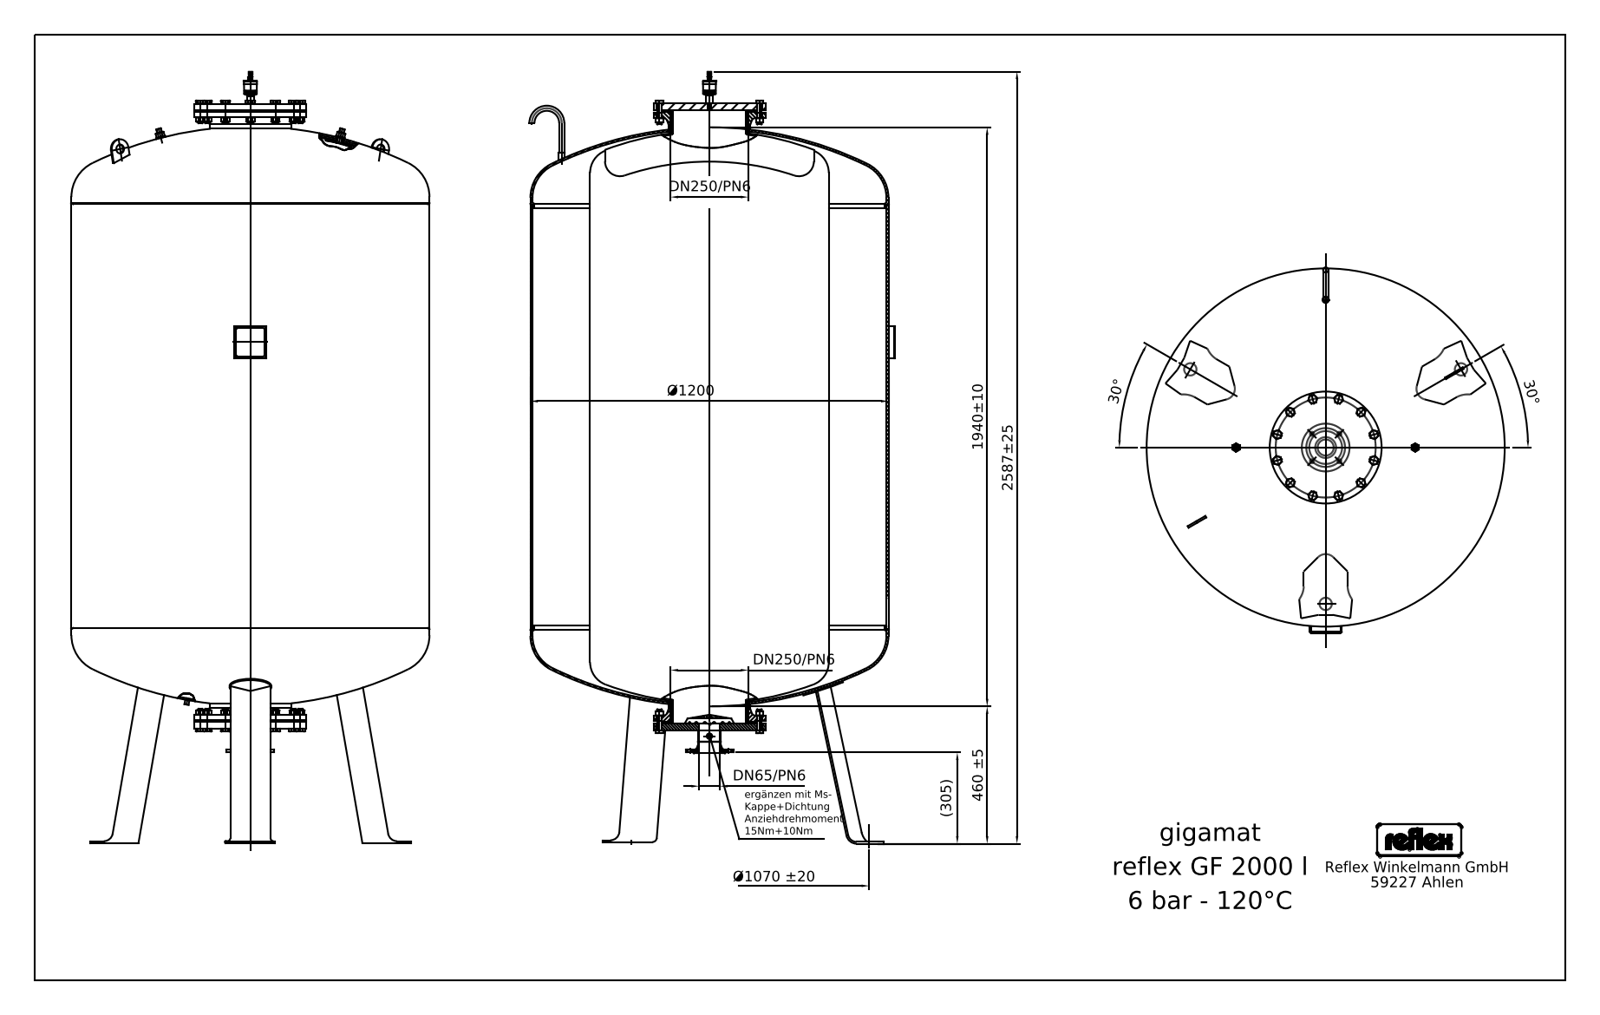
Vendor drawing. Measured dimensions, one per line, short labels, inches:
written by: Mechanical Desktop 2008 (CONFIG_CONTROL_DESIGN)
unit: in
bodies: 20 solids, 863 faces (529 planar, 214 cylindrical, 120 other)
size: 101.85 × 47.244 × 47.244
volume: 123 400 in³; area: 23 140 in²
holes: 1× ⌀1.181, 1× ⌀10.252
bosses: 12× ⌀0.63, 2× ⌀0.654, 2× ⌀0.472, 1× ⌀47.244, 1× ⌀14.764, 1× ⌀10.748, 1× ⌀10.724, 1× ⌀2.996
rounds: 18× R0.984, 4× R0.332, 3× R0.133, 3× R0.354, 2× R0.227, 2× R0.398, 2× R0.548, 2× R0.555
face distances: 56.299, 0.866, 81.693, 1.063, 80.63, 68.622, 12.323, 69.488, 13.189, 13.071
